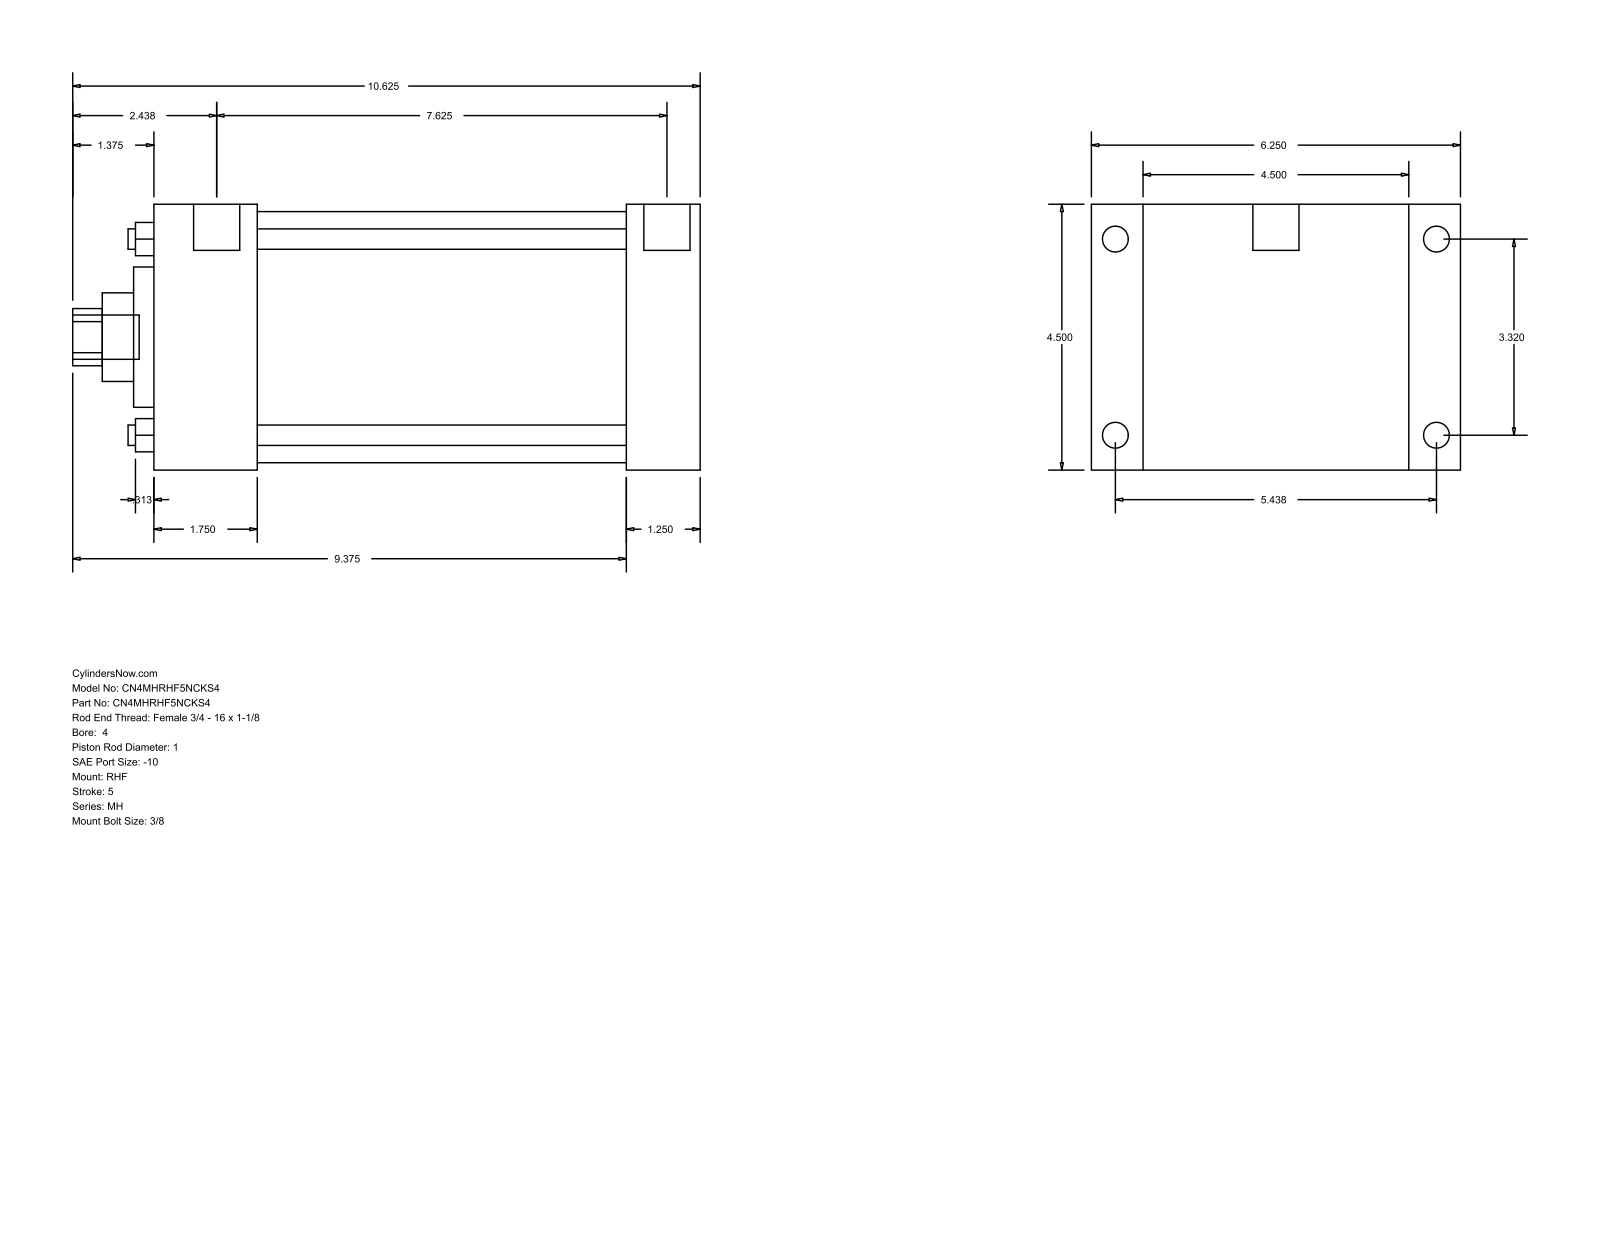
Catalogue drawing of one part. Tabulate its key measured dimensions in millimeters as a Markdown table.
| quantity | value |
| --- | --- |
| part name | MH_RHF__0400_1 |
| STEP written by | GSSL Pune (CONFIG_CONTROL_DESIGN) |
| units | millimeters |
| bodies | 0 solids, 90 faces (61 planar, 29 cylindrical, 0 other) |
| overall size | 269.88 × 158.75 × 114.3 |
| round holes (diameter × count) | 8.76 × 4, 25.4 × 1, 38.1 × 1, 60.33 × 1, 107.95 × 1 |
| round bosses / shafts (diameter × count) | 11.13 × 4, 8.73 × 4, 19.84 × 2, 19.05 × 1 |
| partial cylindrical surfaces (radius × count) | 12.29 × 1 |
| main face-to-face distances | 114.3, 234.96, 203.2, 31.76, 22.23, 136.53, 158.74, 44.46, 190.5, 158.76 |
| hole center spacings | 59.62, 84.32, 119.25 |
